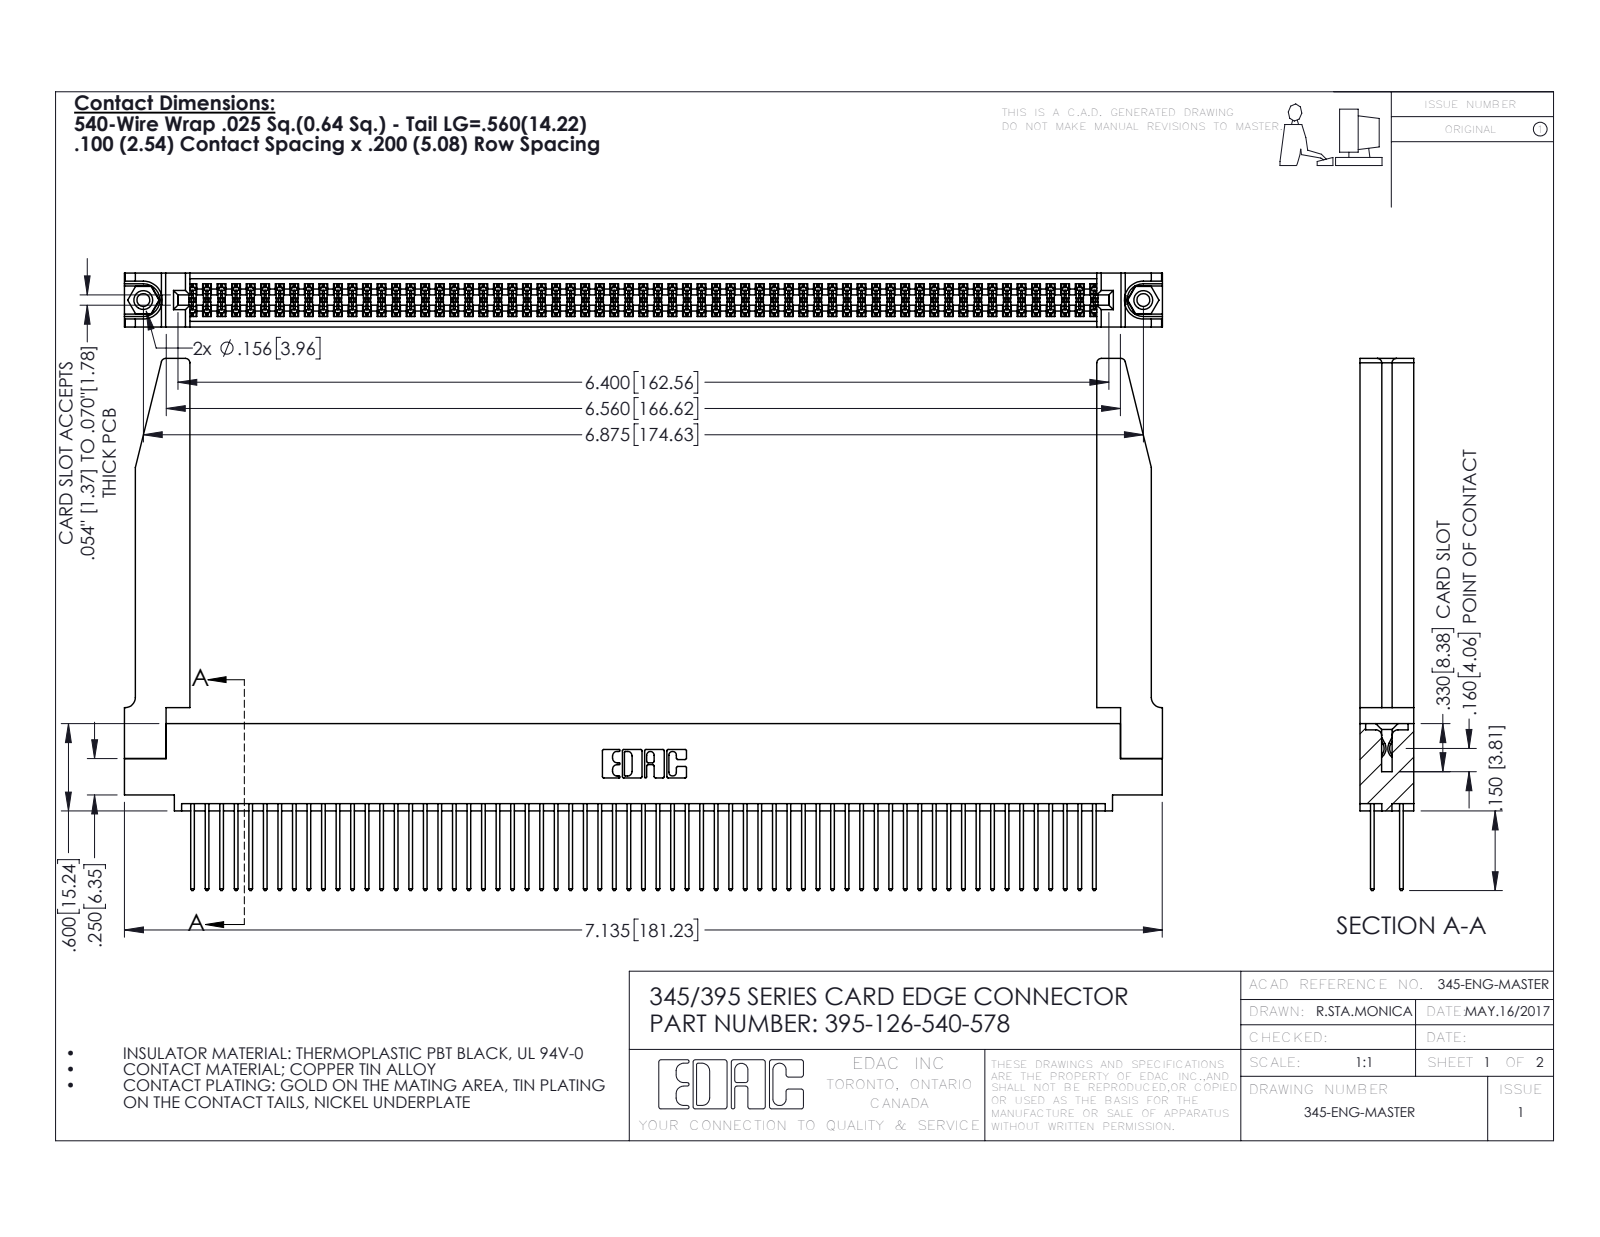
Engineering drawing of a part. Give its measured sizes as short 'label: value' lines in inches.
name: 345 Part_0.110 Offset - 0.156 Dia-TH; 395-126-540-578; 345-292-001_345-293-140; 345-250-001_345-250-001-102 (+1 more)
written by: SolidWorks 2016 (CONFIG_CONTROL_DESIGN)
unit: in
bodies: 131 solids, 6664 faces (4384 planar, 2228 cylindrical, 52 other)
size: 7.136 × 3.657 × 0.37
volume: 1.585 in³; area: 56.52 in²
holes: 2× ⌀0.089, 2× ⌀0.125, 2× ⌀0.156, 1× ⌀0.064
bosses: 2× ⌀0.155
rounds: 189× R0.006, 126× R0.01, 22× R0.01, 8× R0.03, 6× R0.007, 6× R0.031, 3× R0.026, 2× R0.014
face distances: 0.072, 0.298, 0.37, 0.2, 0.098, 0.272, 0.025, 0.225, 0.175, 0.148
hole spacings: 0.27, 6.639, 6.875
